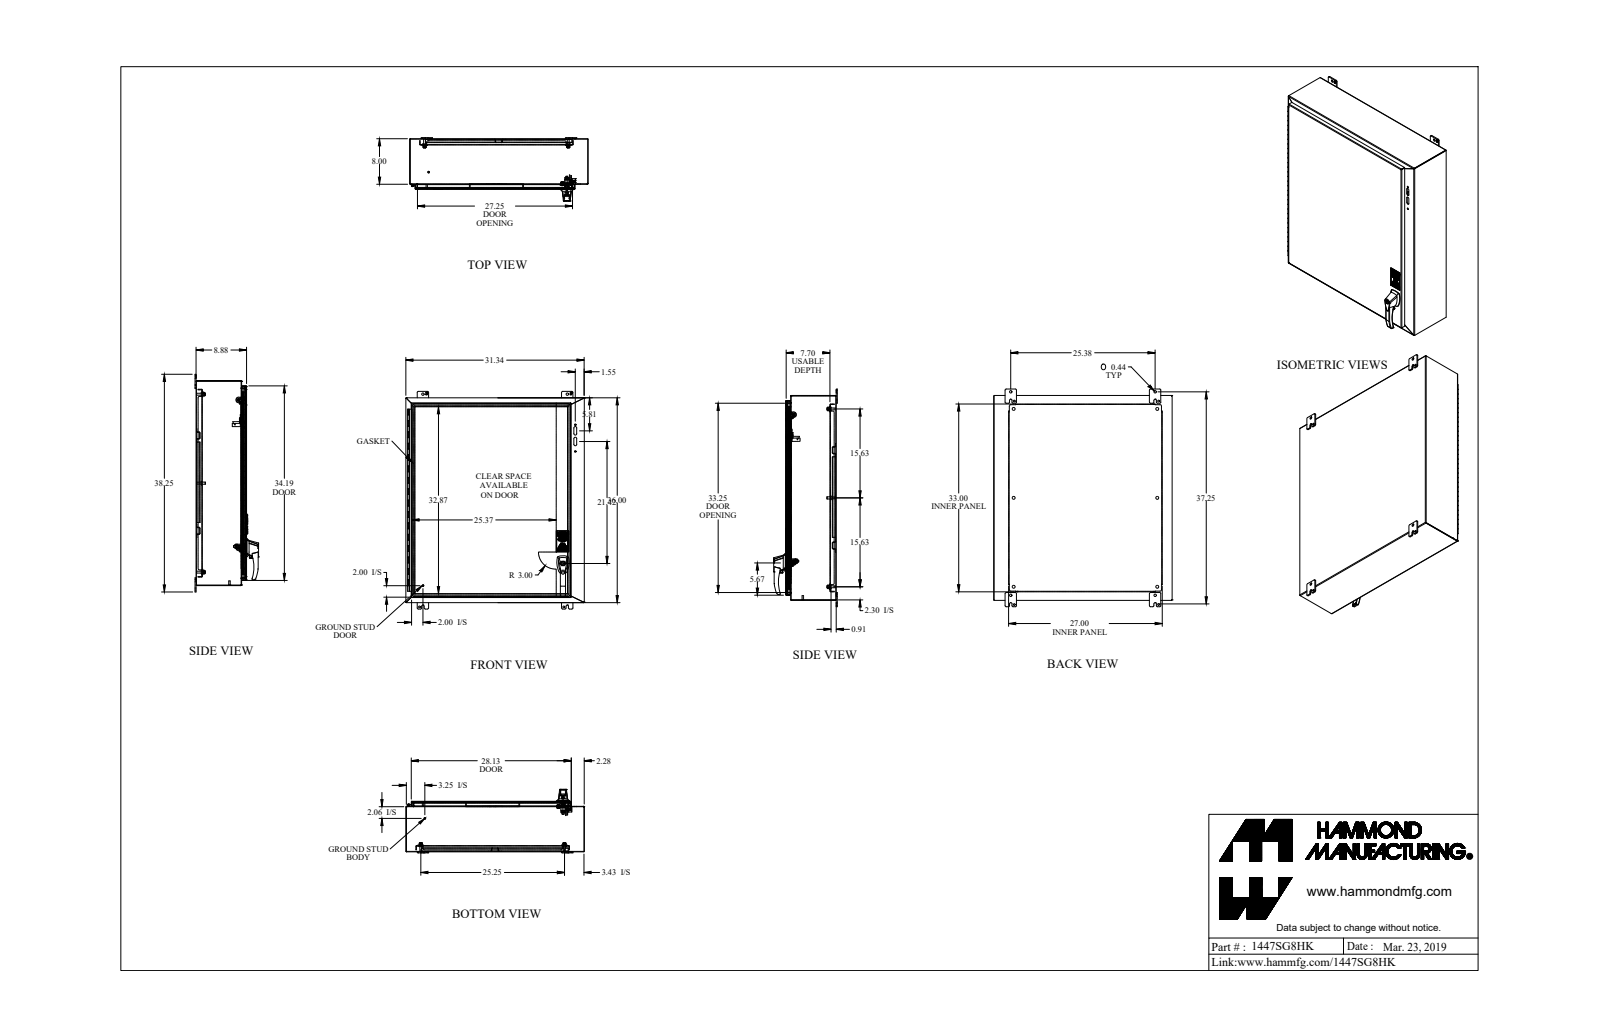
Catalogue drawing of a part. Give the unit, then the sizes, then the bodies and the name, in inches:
Units: inches
Overall size (bounding box): 38.25 × 31.375 × 11.177
Round holes (diameter × count): ⌀0.5 ×6, ⌀0.313 ×5, ⌀0.176 ×4, ⌀0.307 ×4, ⌀0.437 ×4, ⌀0.445 ×4, ⌀0.156 ×2, ⌀0.173 ×2, ⌀0.215 ×2, ⌀0.25 ×2, ⌀0.265 ×2, ⌀0.281 ×2
Round bosses / shafts (diameter × count): ⌀0.375 ×10, ⌀0.25 ×7, ⌀1 ×6, ⌀0.65 ×6, ⌀0.33 ×6, ⌀0.156 ×4, ⌀0.5 ×2, ⌀0.402 ×2
Partial cylindrical surfaces — rounded edges, fillets, slot ends (radius × count): R0.187 ×32, R0.079 ×28, R0.25 ×20, R0.007 ×16, R0.125 ×13, R0.115 ×12, R0.03 ×10, R0.151 ×8
Main face-to-face distances: 0.072, 8.803, 8.731, 8.875, 0.095, 7.771, 7.699, 1.032, 1.104, 7.866
Hole centre spacings: 25.25, 15.625, 25.375, 29.694, 1.111, 1.735, 1.736, 1.855
Volume: 399.6 in³ · Surface area: 10 120 in²
Bodies: 58 solids, 1381 faces (849 planar, 409 cylindrical, 123 other)
Part name (STEP PRODUCT): 1447SG8HK
STEP written by: SolidWorks 2019 (AUTOMOTIVE_DESIGN)
